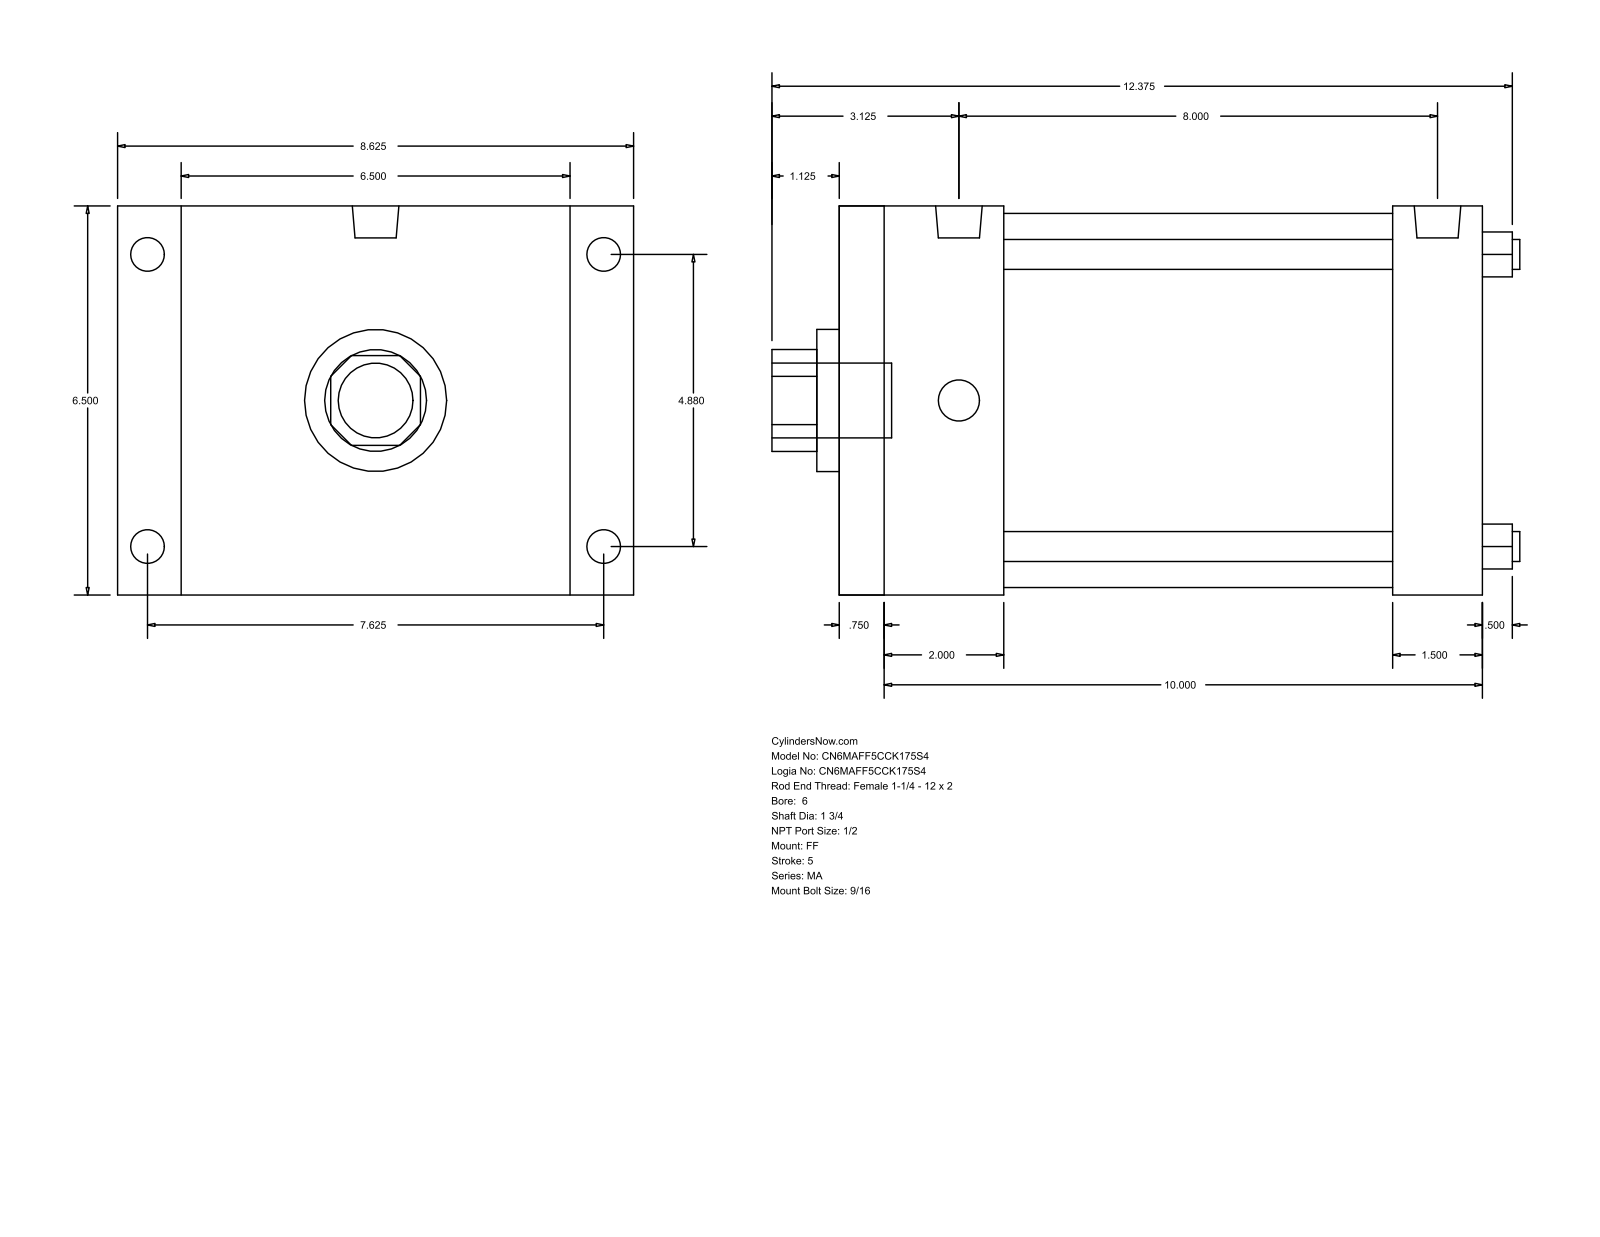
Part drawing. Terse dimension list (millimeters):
name: MA_FF__0600_1.75
written by: GSSL Pune (CONFIG_CONTROL_DESIGN)
unit: mm
bodies: 0 solids, 92 faces (64 planar, 28 cylindrical, 0 other)
size: 317.5 × 219.07 × 165.1
holes: 4× ⌀12.7, 1× ⌀44.45, 1× ⌀60.33, 1× ⌀158.75
bosses: 4× ⌀17.46, 4× ⌀14.29, 2× ⌀19.77, 1× ⌀31.75
rounds: 1× R21.63
face distances: 165.1, 273.05, 19.05, 254, 50.8, 215.9, 38.1, 69.85, 203.2, 234.95
hole spacings: 87.65, 123.96, 175.31
